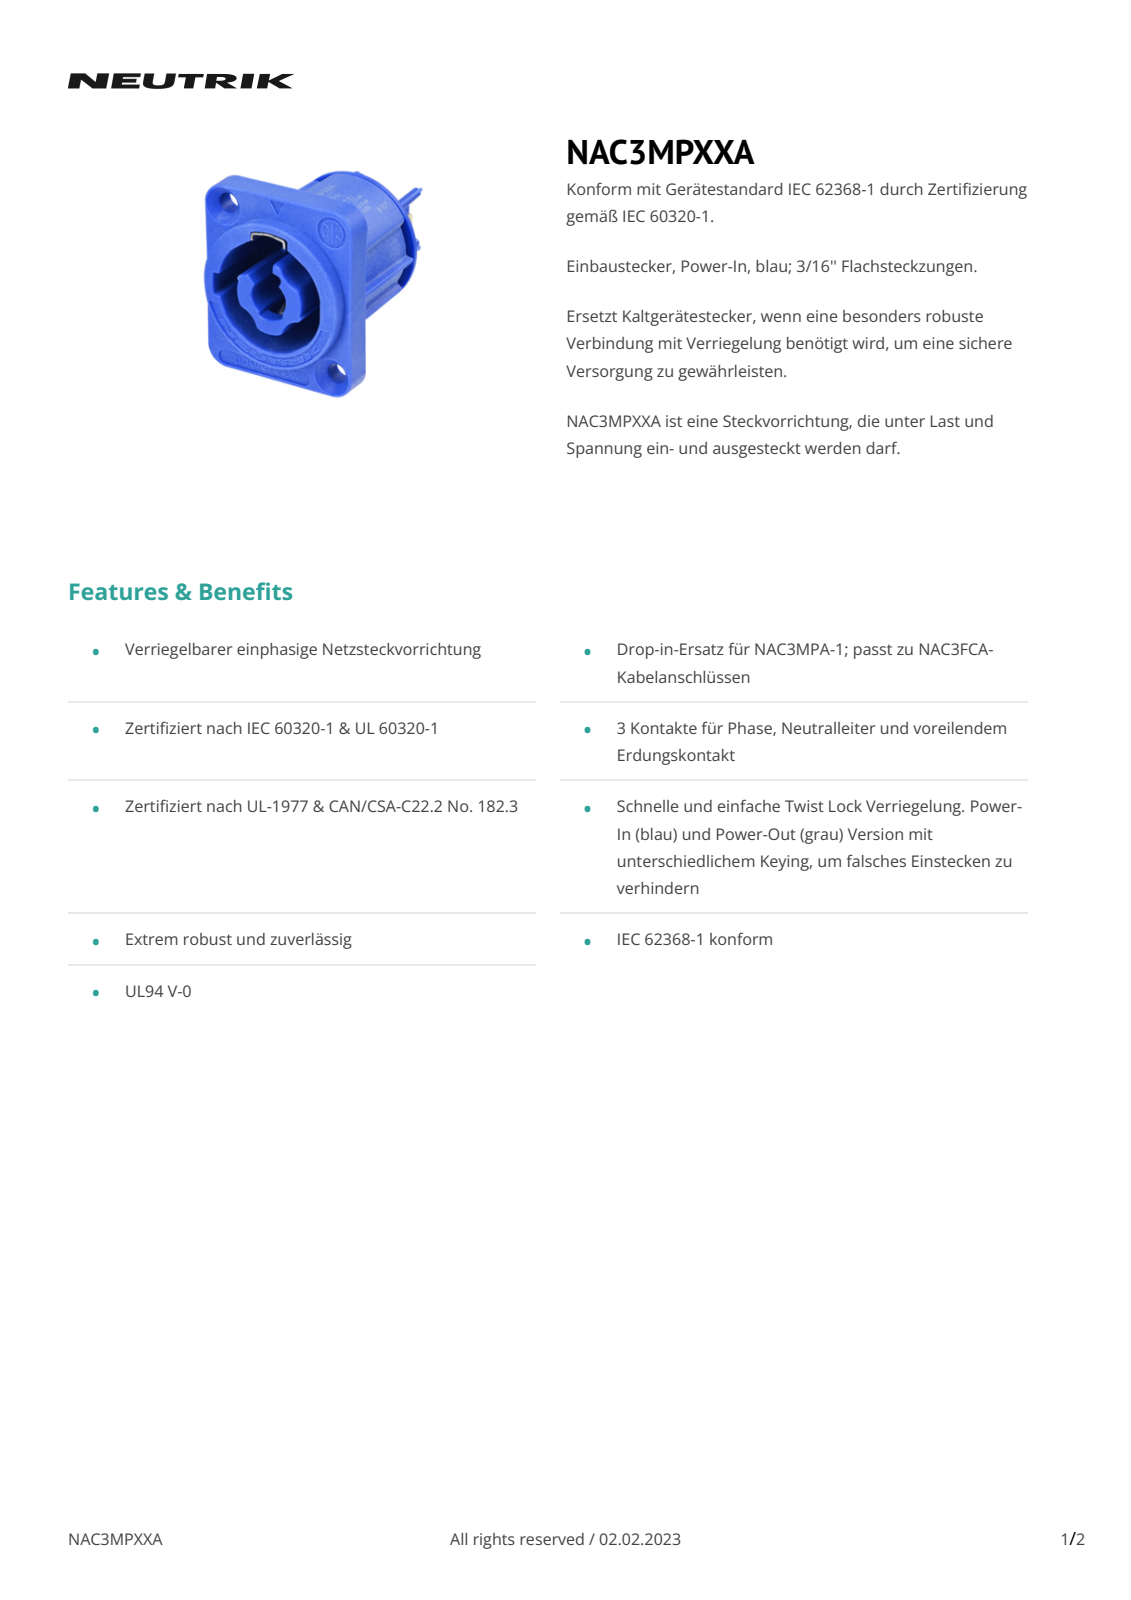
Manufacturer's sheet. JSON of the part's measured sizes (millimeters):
{"part_name": "NAC3MPXXA", "step_written_by": "CREO PARAMETRIC BY PTC INC, 2019080 (CONFIG_CONTROL_DESIGN)", "units": "millimeters", "bodies": {"solids": 1, "faces": 1245, "planar": 385, "cylindrical": 195, "other": 665}, "overall_size": [37.1, 30.9, 25.9], "volume_mm3": 10810, "surface_area_mm2": 6440, "round_holes": [[1.4, 2], [6, 2], [4.2, 1], [5, 1]], "round_bosses_or_shafts": [[19.6, 1], [3.65, 1]], "partial_cylinders_radius": [[0.2, 61], [0.5, 21], [0.3, 20], [0.25, 15], [0.21, 9], [0.14, 7], [0.28, 3], [0.15, 2]], "face_to_face_distances": [4.55, 2.5, 7.05, 23.6, 23.55, 4.5, 19.05, 2.55, 26.1, 20.45], "hole_center_spacings": [20.83, 10.96, 19, 24, 30.61]}
